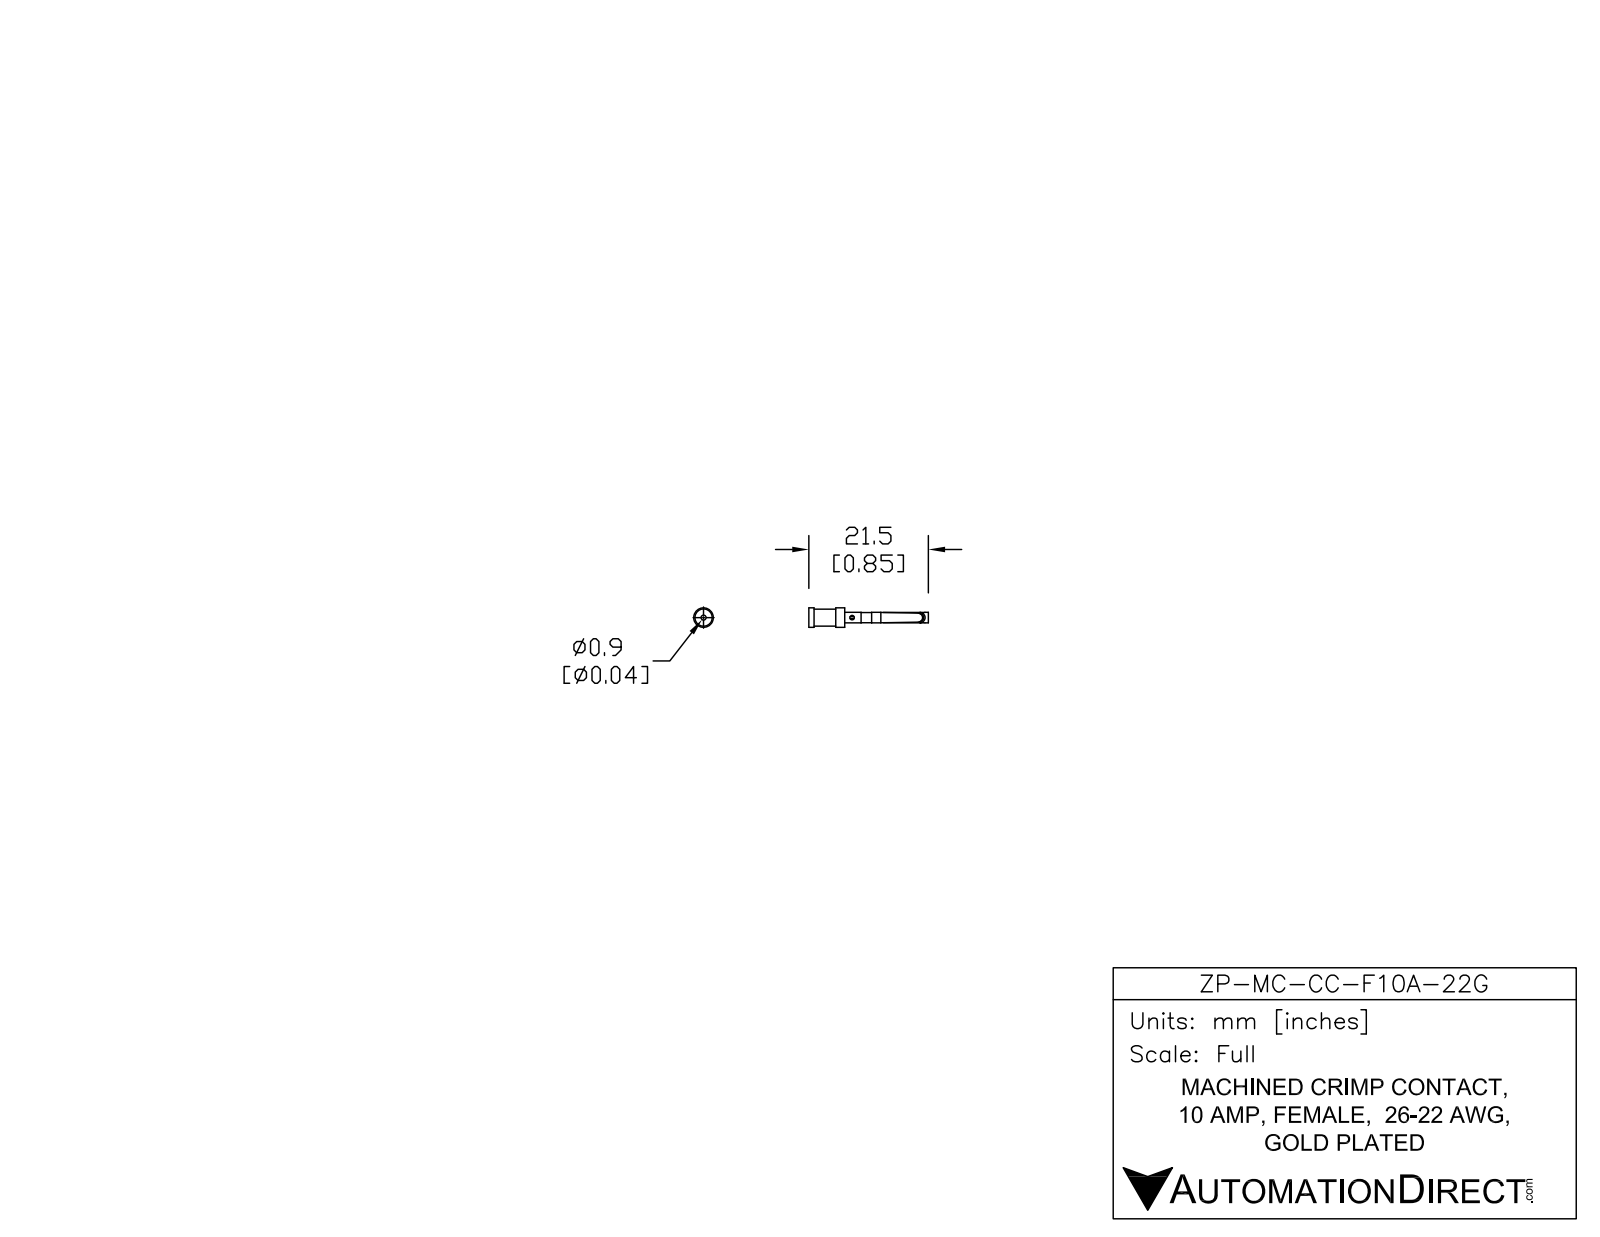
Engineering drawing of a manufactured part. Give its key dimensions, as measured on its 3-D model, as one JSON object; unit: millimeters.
{"part_name": "ZP-MC-CC-F10A-22G", "step_written_by": "SolidWorks 2014 (AUTOMOTIVE_DESIGN)", "units": "millimeters", "bodies": {"solids": 1, "faces": 55, "planar": 28, "cylindrical": 18, "other": 9}, "overall_size": [21.68, 3.52, 3.52], "volume_mm3": 86, "surface_area_mm2": 299, "round_holes": [[0.8, 1], [0.9, 1], [1.64, 1]], "round_bosses_or_shafts": [[3.52, 1], [2.68, 1], [2.48, 1], [2.01, 1]], "face_to_face_distances": [10, 11.68, 1.58, 5.51, 3.93, 6.51, 4.93, 1, 1.84, 3.49]}
